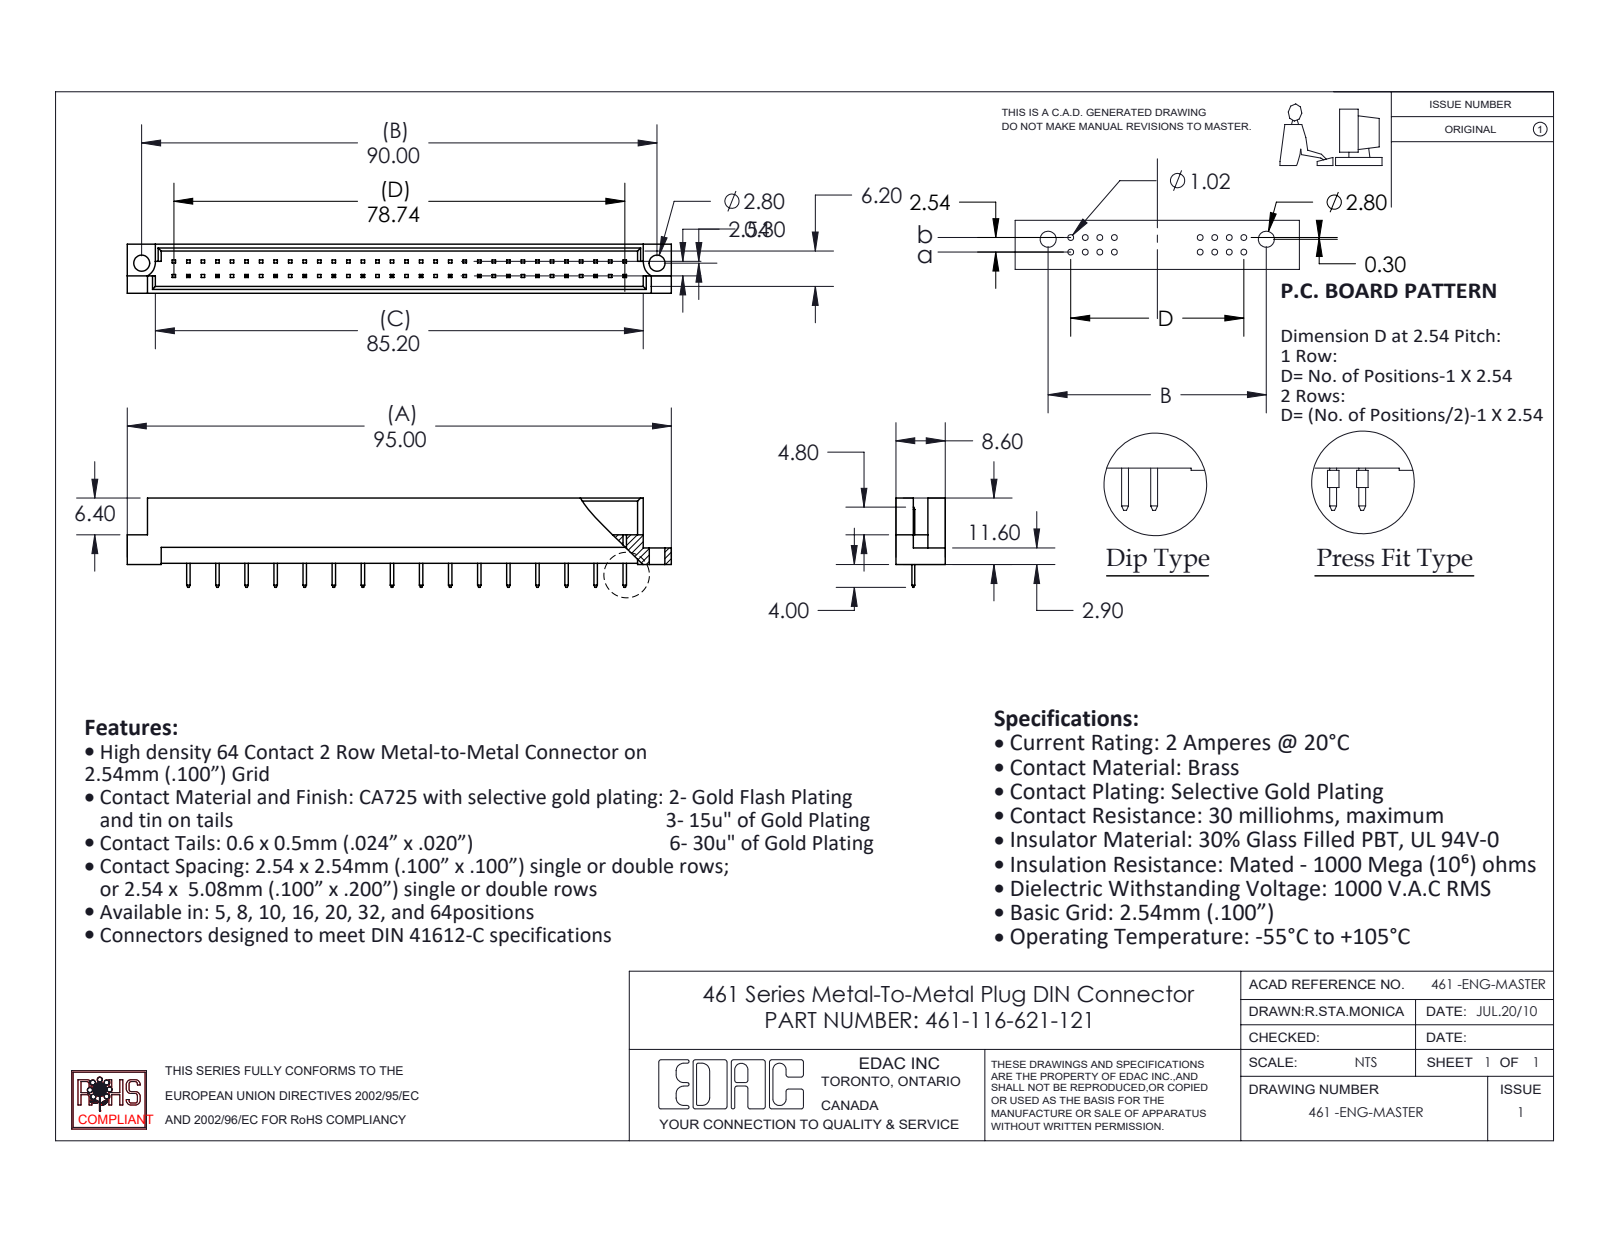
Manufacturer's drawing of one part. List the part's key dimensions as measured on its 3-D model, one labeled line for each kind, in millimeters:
Part name (STEP PRODUCT): 461-290_21; 461-116-621-221; 461 Part_64
STEP written by: SolidWorks 2020 (CONFIG_CONTROL_DESIGN)
Units: millimetres
Bodies: 17 solids, 529 faces (522 planar, 7 cylindrical, 0 other)
Overall size (bounding box): 95 × 15.6 × 8.6
Volume: 4 722 mm³ · Surface area: 6 158 mm²
Round holes (diameter × count): ⌀2.8 ×2
Partial cylindrical surfaces — rounded edges, fillets, slot ends (radius × count): R2.8 ×2
Main face-to-face distances: 1.2, 7.4, 8.6, 6.2, 5, 3.28, 5.32, 2.08, 4.12, 2.78
Hole centre spacings: 90
